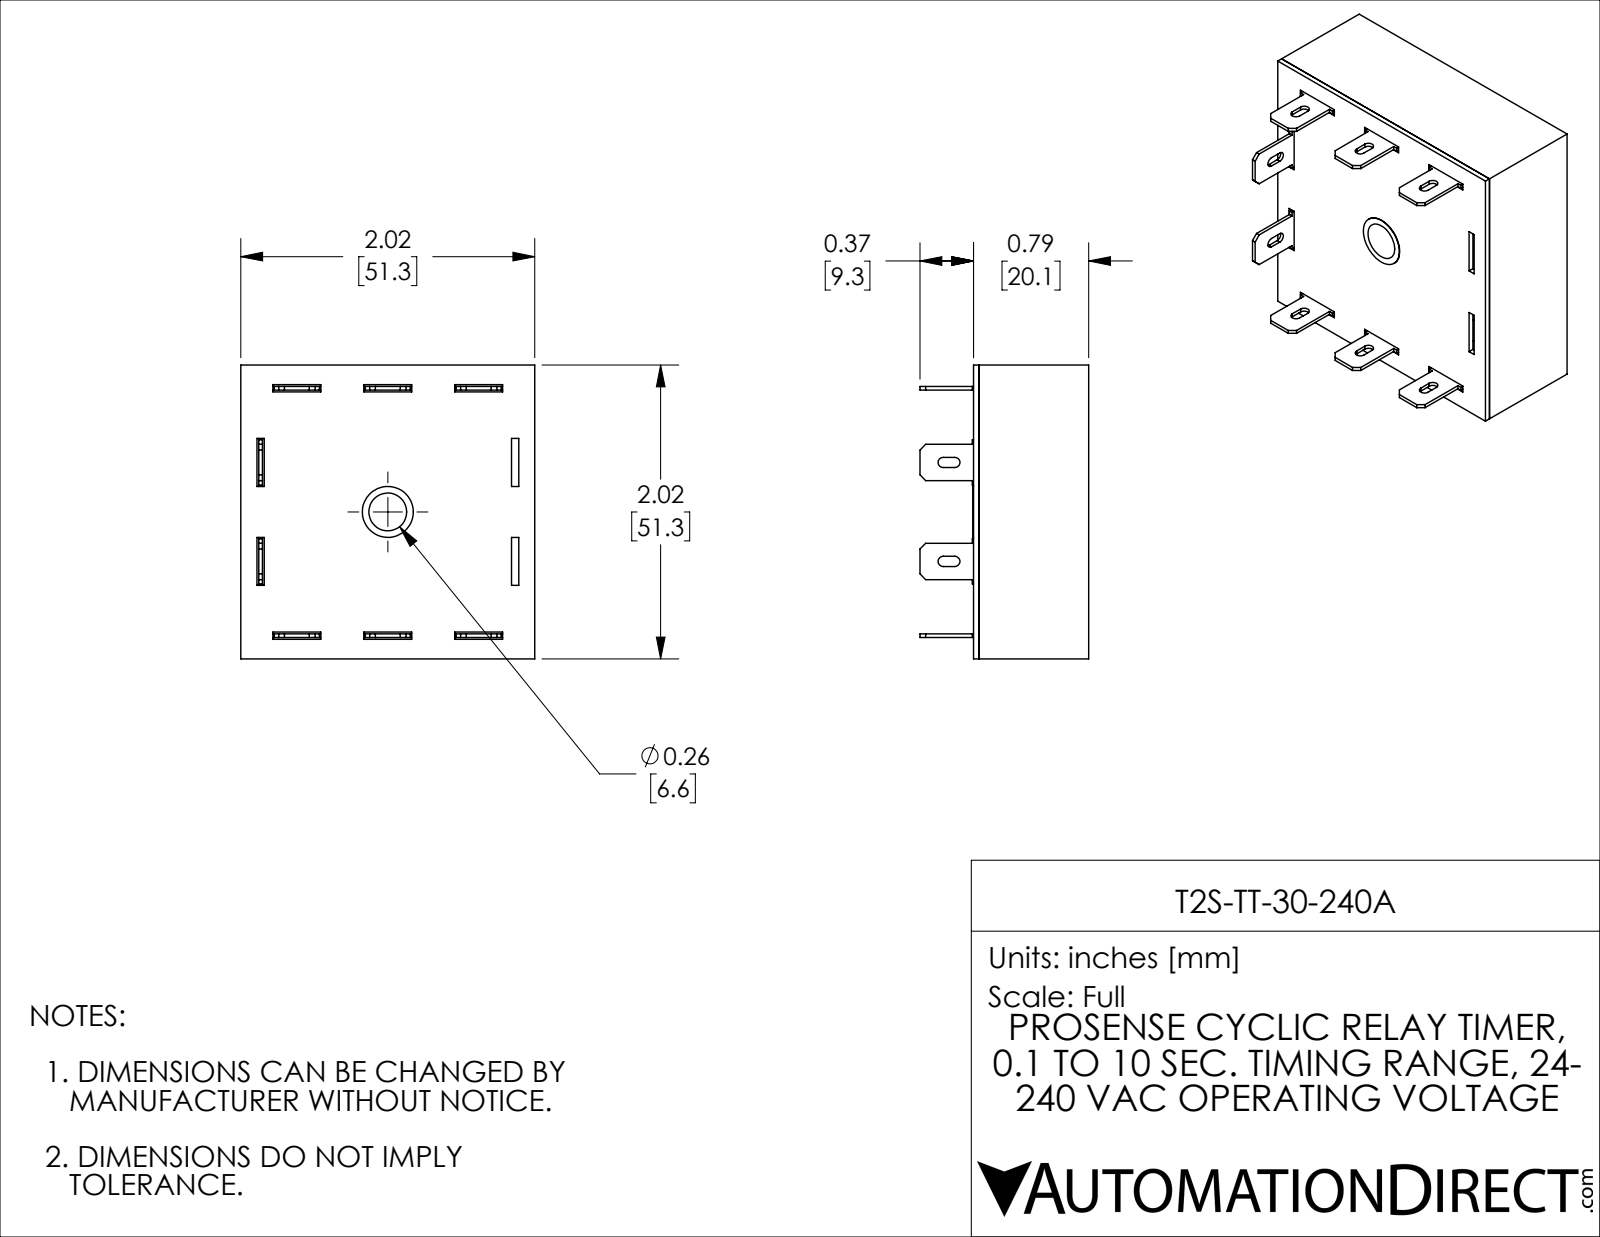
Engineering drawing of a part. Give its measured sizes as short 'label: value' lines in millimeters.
name: T2S-TT-30-240A
written by: SolidWorks 2021 (CONFIG_CONTROL_DESIGN)
unit: mm
bodies: 10 solids, 256 faces (234 planar, 20 cylindrical, 2 other)
size: 51.31 × 51.31 × 29.46
volume: 11 042 mm³; area: 22 819 mm²
holes: 1× ⌀8.89
rounds: 10× R0.89
face distances: 1.14, 50.16, 19.15, 20.12, 0.97, 18.01, 18.98, 51.3, 49.02, 3.74
